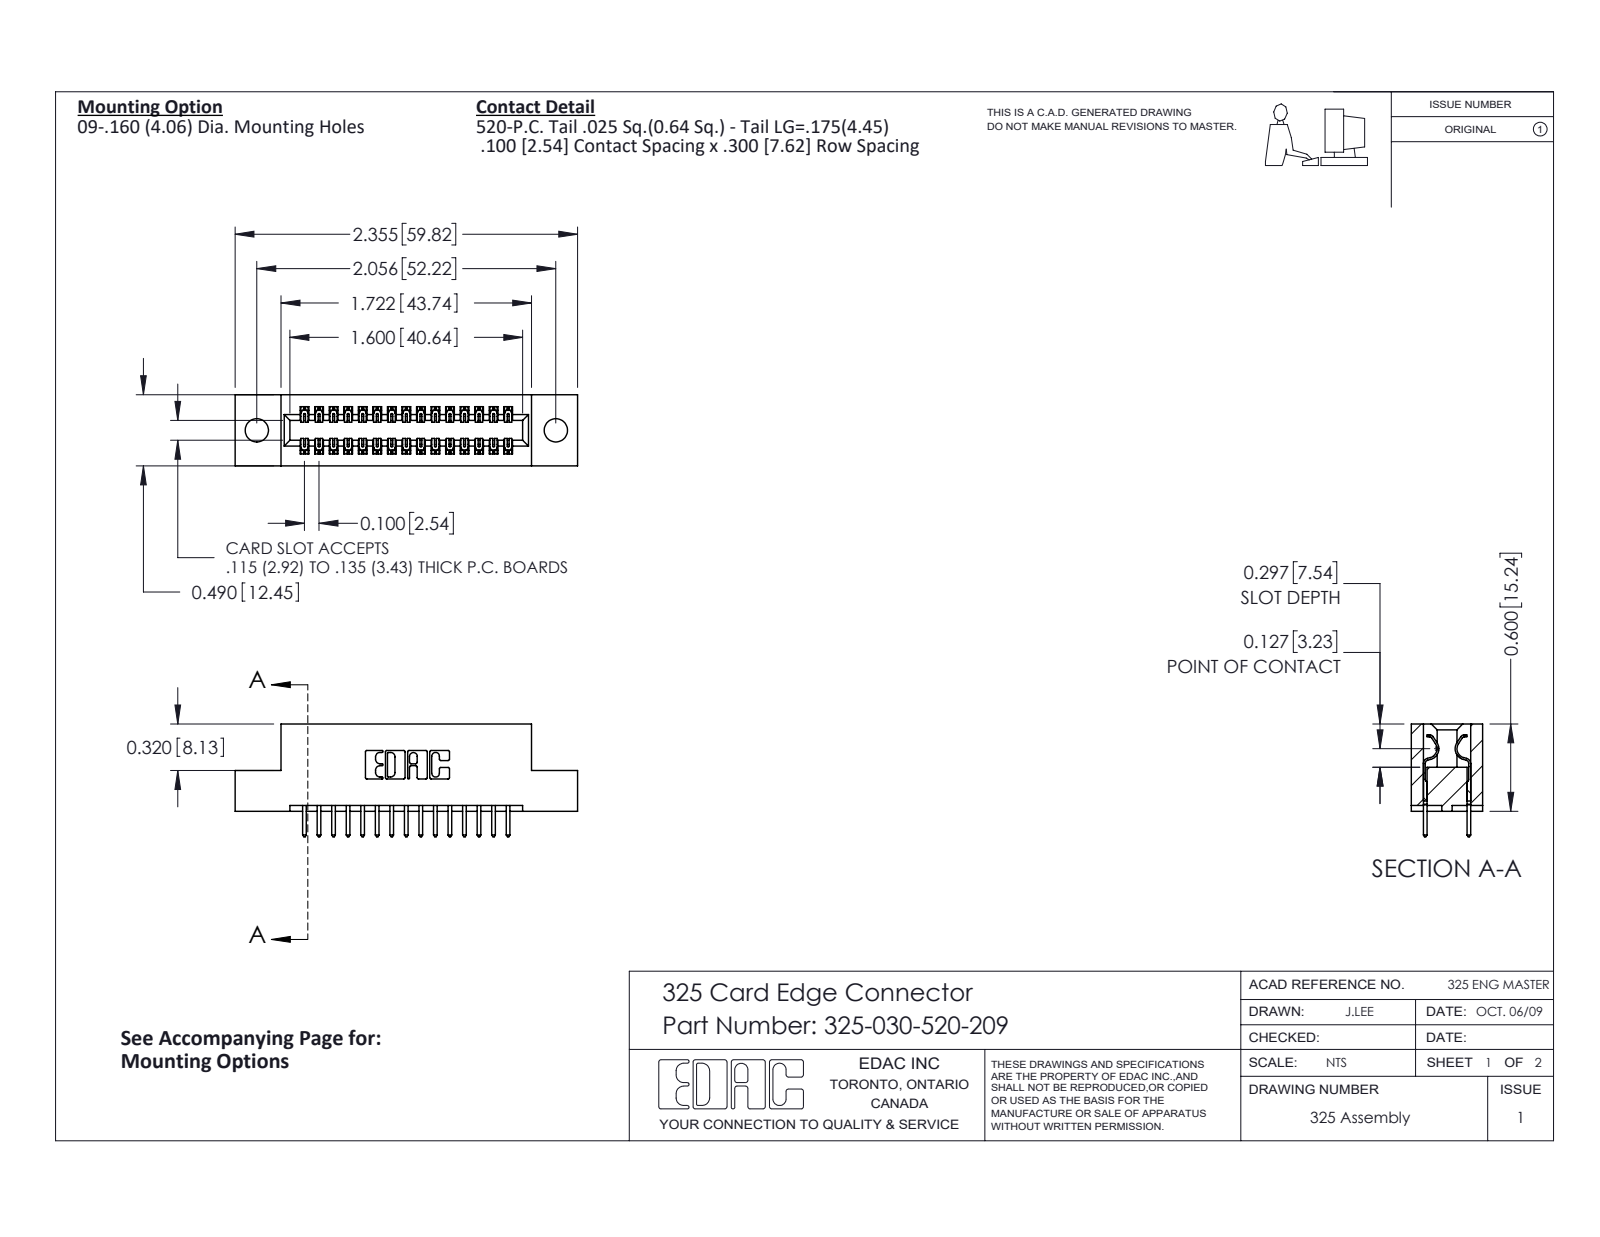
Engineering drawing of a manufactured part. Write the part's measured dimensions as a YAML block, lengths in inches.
part_name: "325 Part_.160 TH; 325-030-520-209; 325-292-001_325-293-120"
step_written_by: "SolidWorks 2016 (CONFIG_CONTROL_DESIGN)"
units: inches
bodies: {solids: 31, faces: 1674, planar: 1150, cylindrical: 524, other: 0}
overall_size: [2.355, 0.775, 0.49]
volume: 0.442
surface_area: 12.38
round_holes:
  - {diameter: 0.16, count: 2}
partial_cylinders:
  - {radius: 0.006, count: 45}
  - {radius: 0.01, count: 30}
  - {radius: 0.01, count: 22}
  - {radius: 0.007, count: 6}
  - {radius: 0.031, count: 6}
  - {radius: 0.026, count: 3}
  - {radius: 0.014, count: 2}
  - {radius: 0.022, count: 2}
face_to_face_distances: [0.083, 0.407, 0.3, 0.49, 0.107, 0.383, 0.025, 0.325, 0.04, 0.1]
hole_center_spacings: [2.056]
